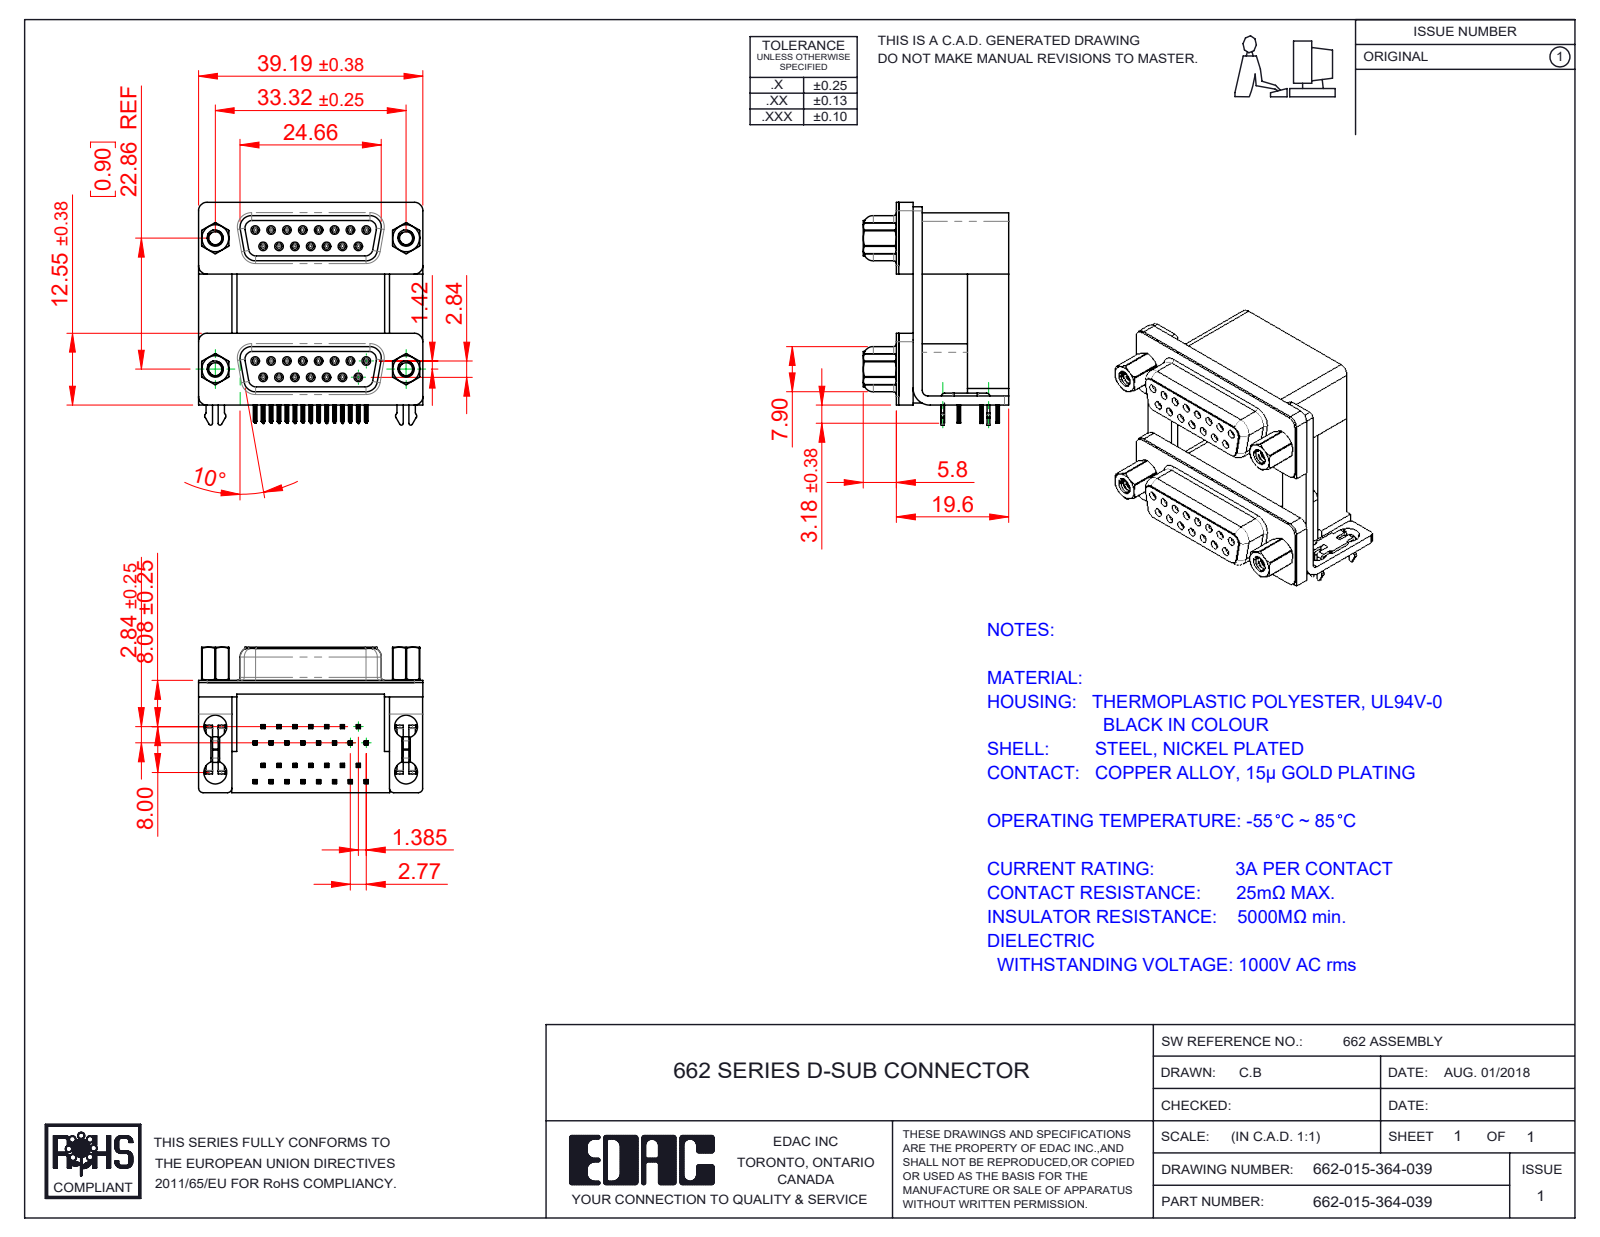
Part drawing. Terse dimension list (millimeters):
name: 662-015-364-039; 662 Housing Lower_15 Contacts; 662 Housing Spacer_15 Contacts H; 662 Shell_15 Contacts (+8 more)
written by: SolidWorks 2020 (CONFIG_CONTROL_DESIGN)
unit: mm
bodies: 47 solids, 5266 faces (2342 planar, 1368 cylindrical, 1556 other)
size: 39.19 × 38.91 × 25.4
volume: 17 213 mm³; area: 19 852 mm²
holes: 30× ⌀0.8, 30× ⌀0.9, 8× ⌀4, 4× ⌀2.26, 4× ⌀2.29, 4× ⌀3.5, 4× ⌀4.8, 4× ⌀5
bosses: 30× ⌀1.2, 4× ⌀4.9, 4× ⌀4.75, 4× ⌀3.9, 4× ⌀2.79
rounds: 242× R0.1, 120× R0.15, 60× R0.35, 30× R0.34, 16× R1.35, 16× R1.5, 14× R0.28, 12× R0.5
face distances: 19.2, 0.4, 22.86, 7.2, 12, 9.5, 16.7, 2.5, 2.9, 10.7
hole spacings: 3.16, 23.03, 2.77, 23.52, 5.54, 8.31, 22.86, 24.32
